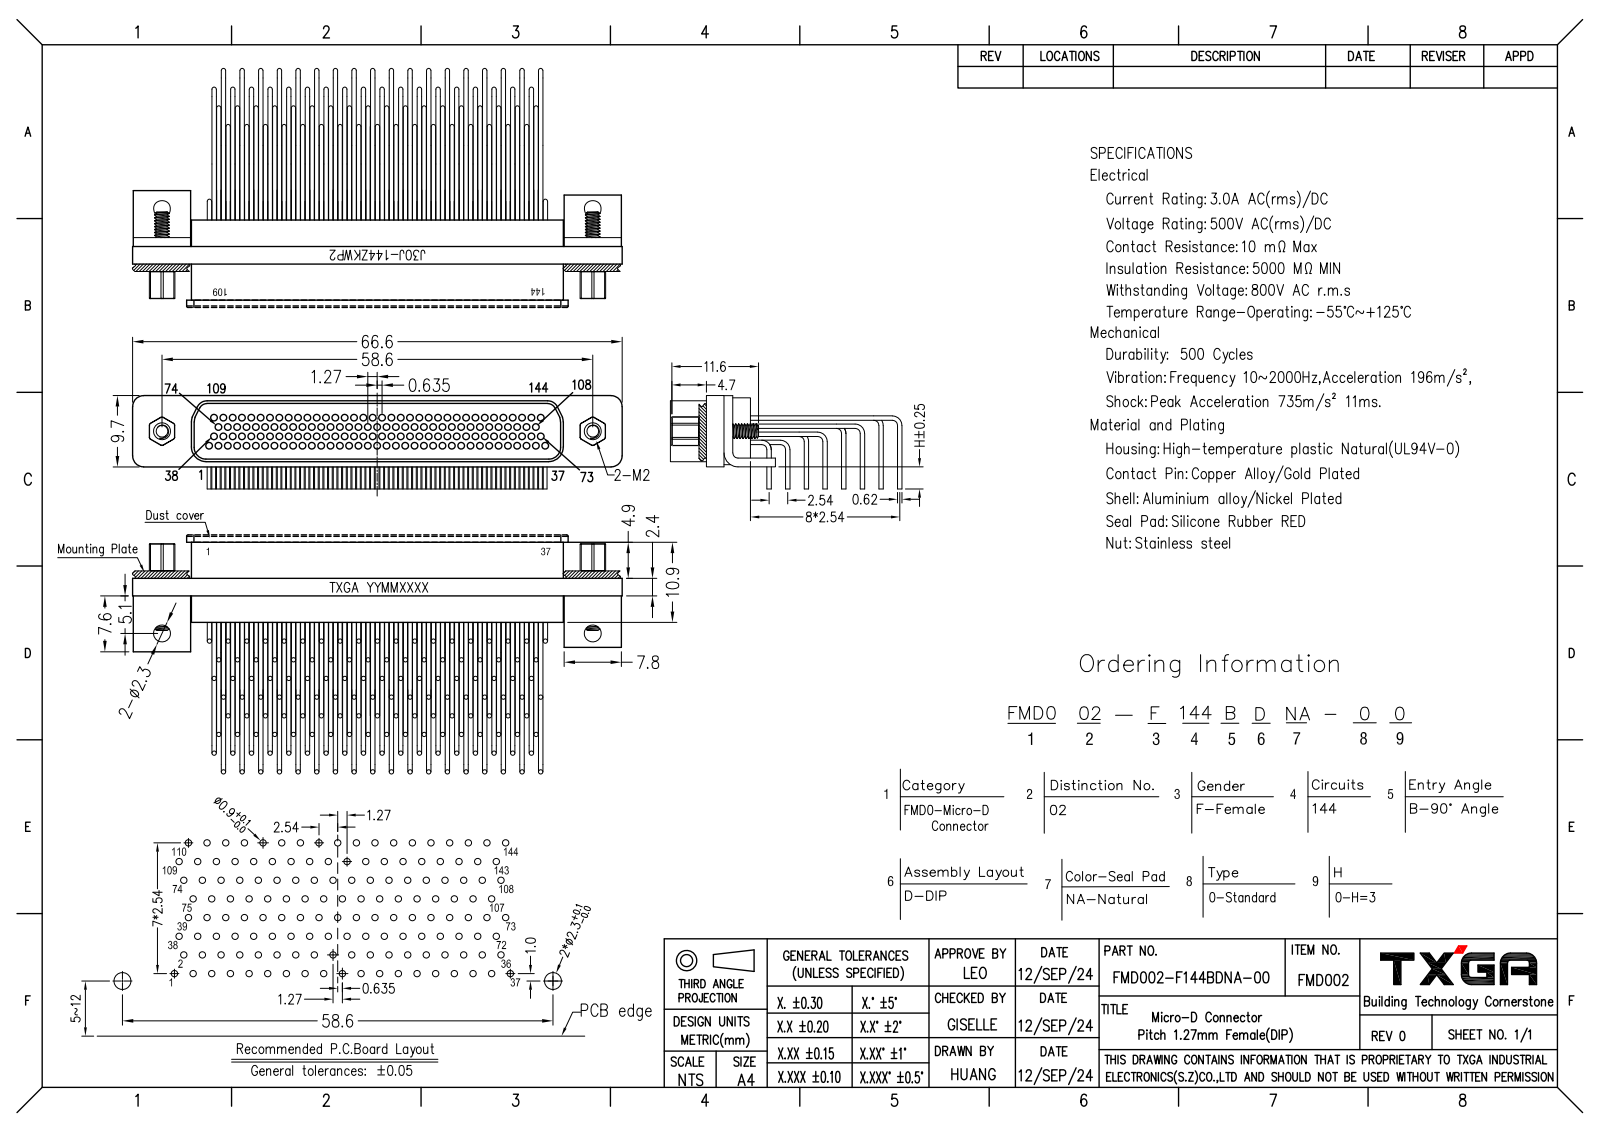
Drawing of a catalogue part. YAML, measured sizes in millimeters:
part_name: "FMD002-F144BDNA-00"
step_written_by: "SolidWorks 2021 (CONFIG_CONTROL_DESIGN)"
units: millimeters
bodies: {solids: 1, faces: 3262, planar: 1061, cylindrical: 1314, other: 887}
overall_size: [66.6, 31.52, 12.7]
volume: 4804
surface_area: 11098
round_holes:
  - {diameter: 0.6, count: 144}
  - {diameter: 1.6, count: 2}
  - {diameter: 1.8, count: 2}
  - {diameter: 2.3, count: 2}
  - {diameter: 3.2, count: 2}
round_bosses_or_shafts:
  - {diameter: 0.8, count: 144}
  - {diameter: 0.6, count: 144}
  - {diameter: 2, count: 2}
partial_cylinders:
  - {radius: 0.3, count: 12}
  - {radius: 1.5, count: 8}
  - {radius: 2.4, count: 6}
  - {radius: 2, count: 4}
  - {radius: 1.7, count: 2}
  - {radius: 0.7, count: 1}
  - {radius: 1.9, count: 1}
face_to_face_distances: [0.7, 8.3, 6, 7.6, 1.4, 8, 9, 8.7, 0.4, 1.1]
hole_center_spacings: [1.27, 2.54, 5.08, 7.62, 3.36, 2.2, 10.16, 3.81]
